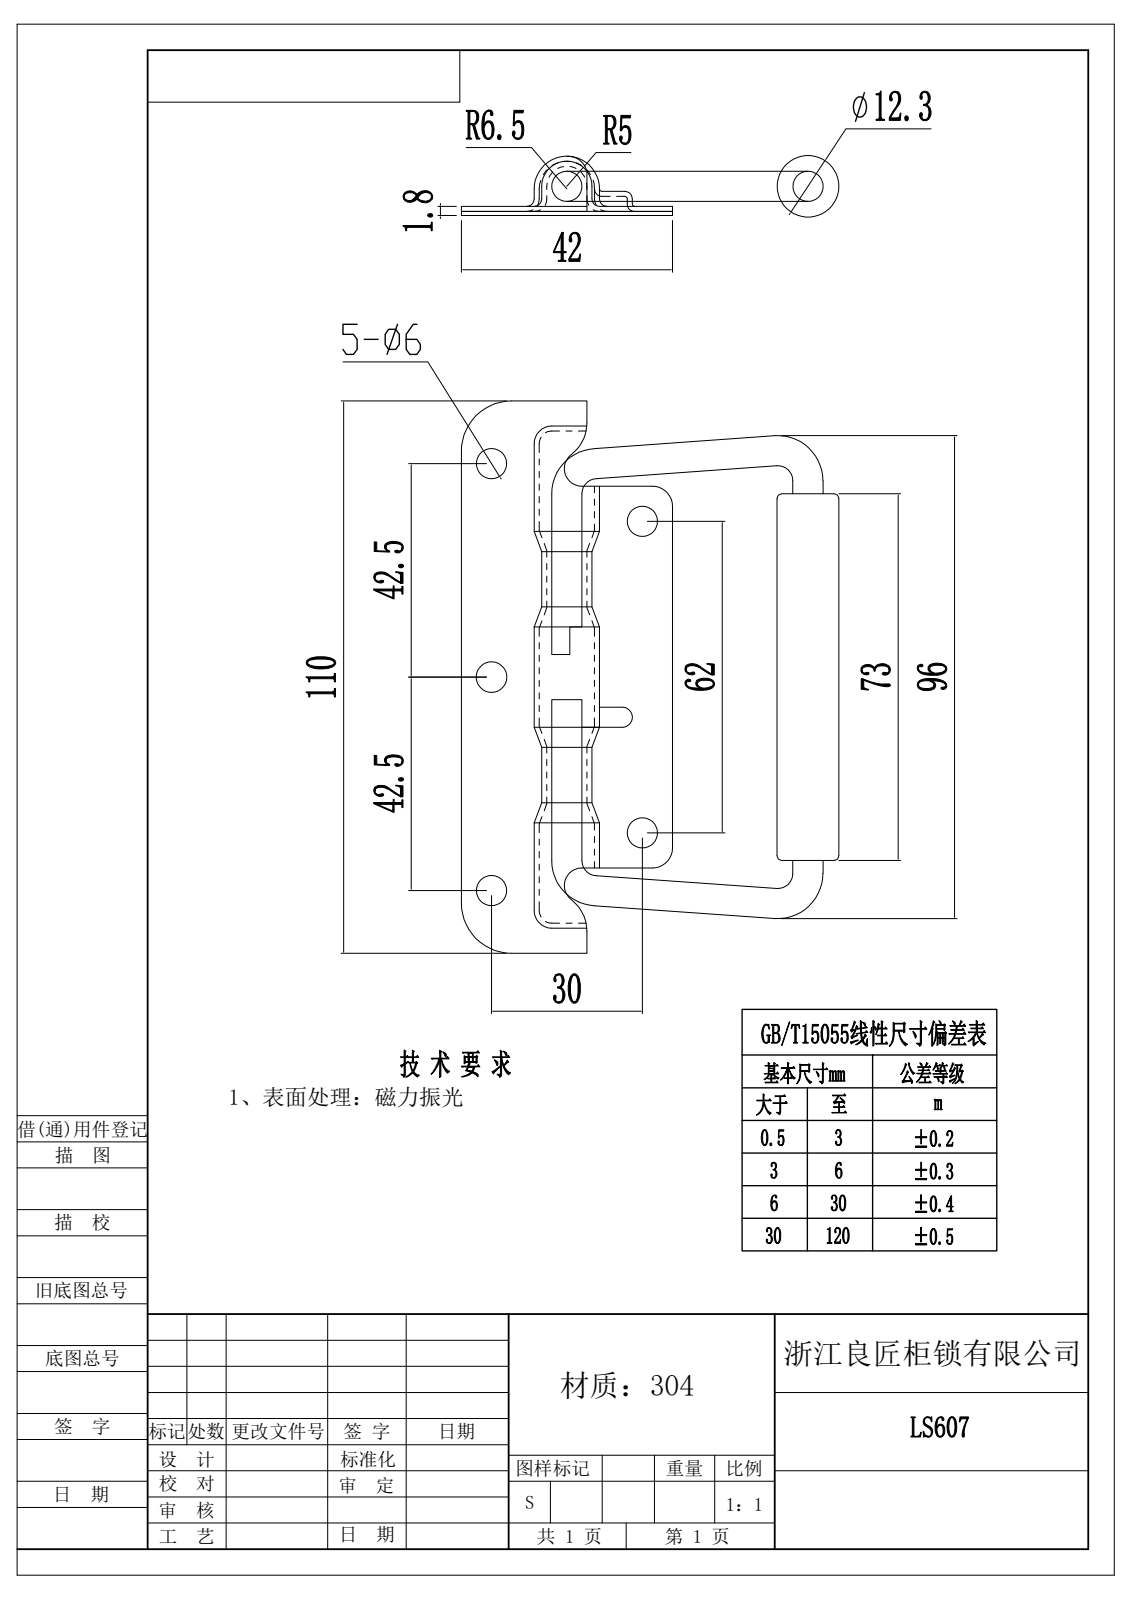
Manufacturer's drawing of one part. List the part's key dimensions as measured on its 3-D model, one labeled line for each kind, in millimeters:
STEP written by: Rhino 8.5 (CONFIG_CONTROL_DESIGN)
Units: millimetres
Bodies: 4 solids, 214 faces (66 planar, 111 cylindrical, 37 other)
Overall size (bounding box): 110 × 69.15 × 12.65
Volume: 16 935 mm³ · Surface area: 28 543 mm²
Round holes (diameter × count): ⌀6 ×6
Round bosses / shafts (diameter × count): ⌀6 ×3, ⌀12.3 ×1, ⌀9 ×1, ⌀5.9 ×1
Partial cylindrical surfaces — rounded edges, fillets, slot ends (radius × count): R0.5 ×14, R1.5 ×13, R1 ×8, R10 ×4, R4 ×3, R3.5 ×2, R8 ×2, R1.05 ×1
Main face-to-face distances: 0.8, 1, 1.8, 15.5, 26.5, 1.5, 12, 13, 10.5, 42
Hole centre spacings: 32.13, 42.5, 43.14, 79.39, 62, 85
